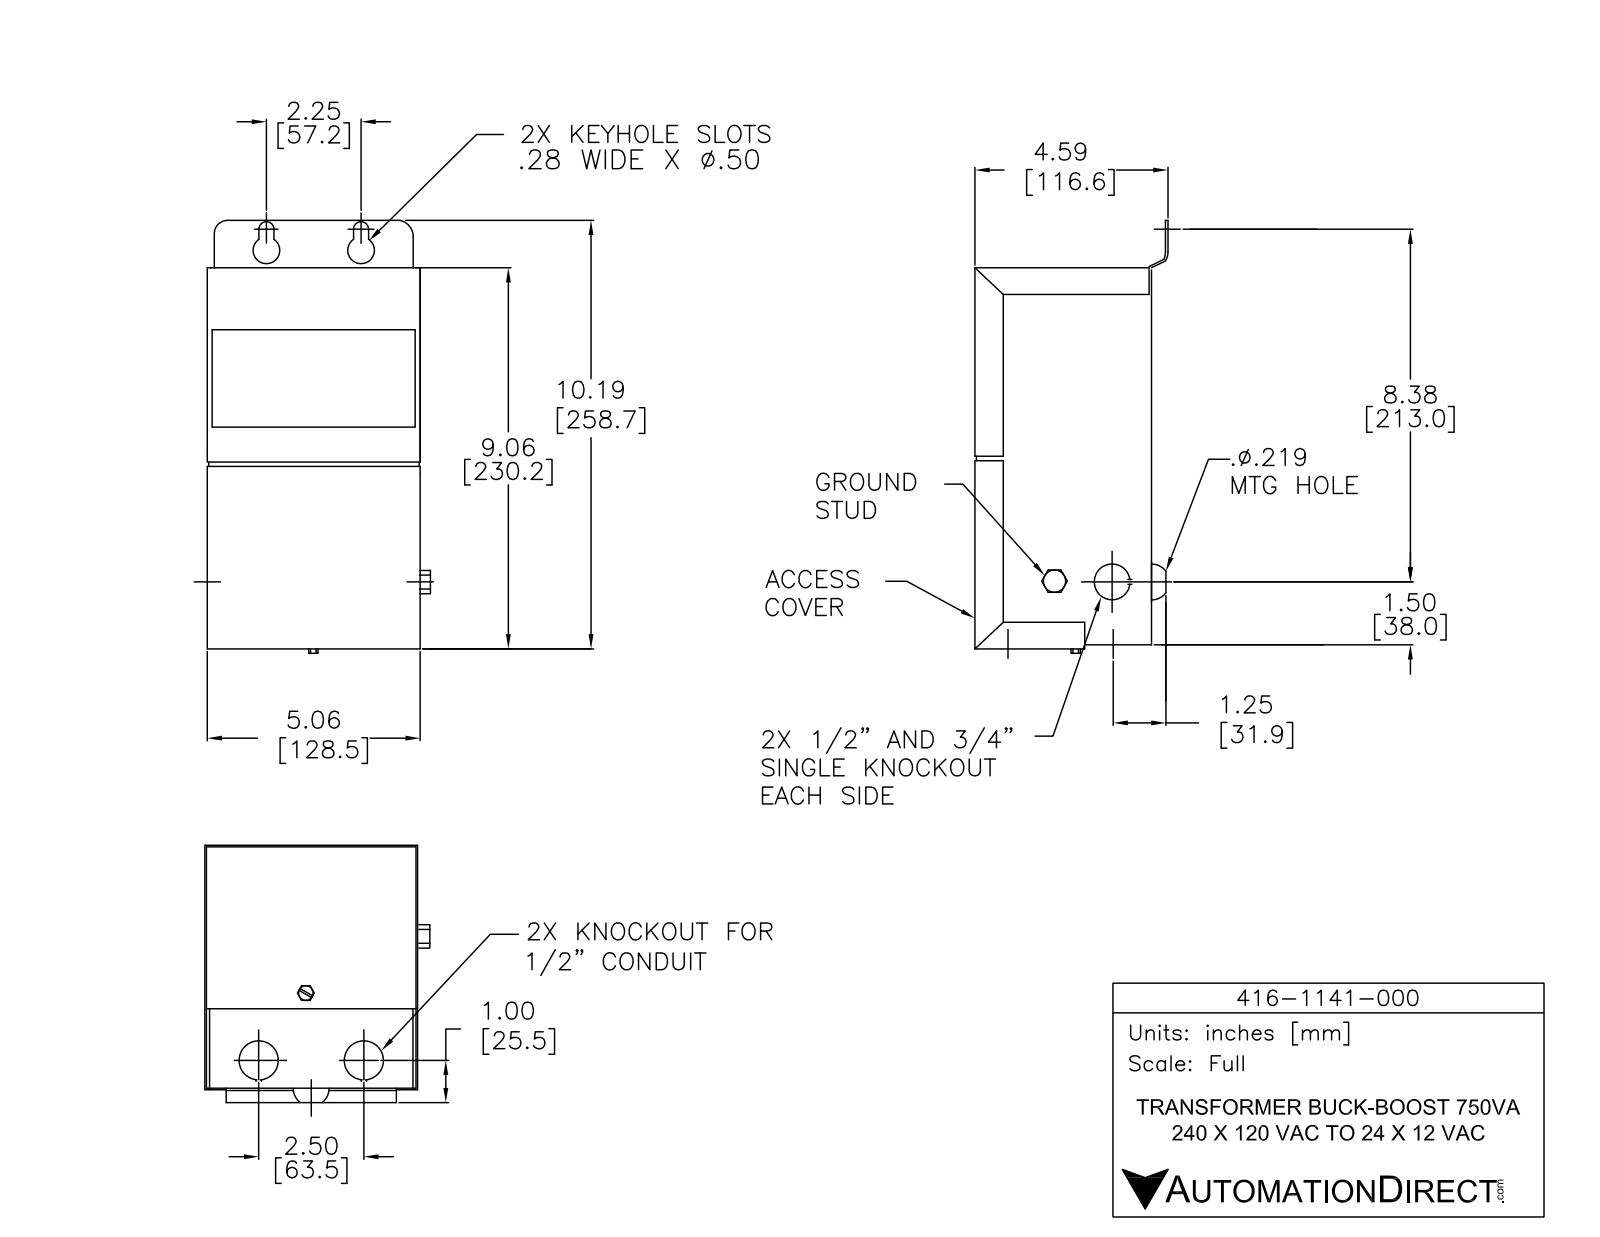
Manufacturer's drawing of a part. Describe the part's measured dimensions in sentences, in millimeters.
The part is named "416-1141-000". Its 3-D file was written by "SolidWorks 2013 (AUTOMOTIVE_DESIGN)". It is 1 solid with 159 faces: 91 planar, 52 cylindrical and 16 other. Overall it measures 261.6 by 131.3 by 116.6 millimeters. Its volume is 3 118 000 cubic millimeters and its surface area 145 400 square millimeters. Round holes: 2 of diameter 12.7, 2 of diameter 22.2, 1 of diameter 5.6, 1 of diameter 5.9, 1 of diameter 7.4, 1 of diameter 22.2. Round bosses or shafts: 1 of diameter 28.6. Partial cylindrical surfaces (rounded edges, fillets, slot ends): 10 of radius 1, 10 of radius 6.4, 2 of radius 3.6, 1 of radius 1.5, 1 of radius 3.8, 1 of radius 4.8. The main face-to-face distances are 106.7, 126.5, 1, 127.5, 106.7, 230.1, 128.5, 229.1, 1, 9.9. The hole center spacings are 43.7, 207.5, 34.8, 57.2, 63.5.
